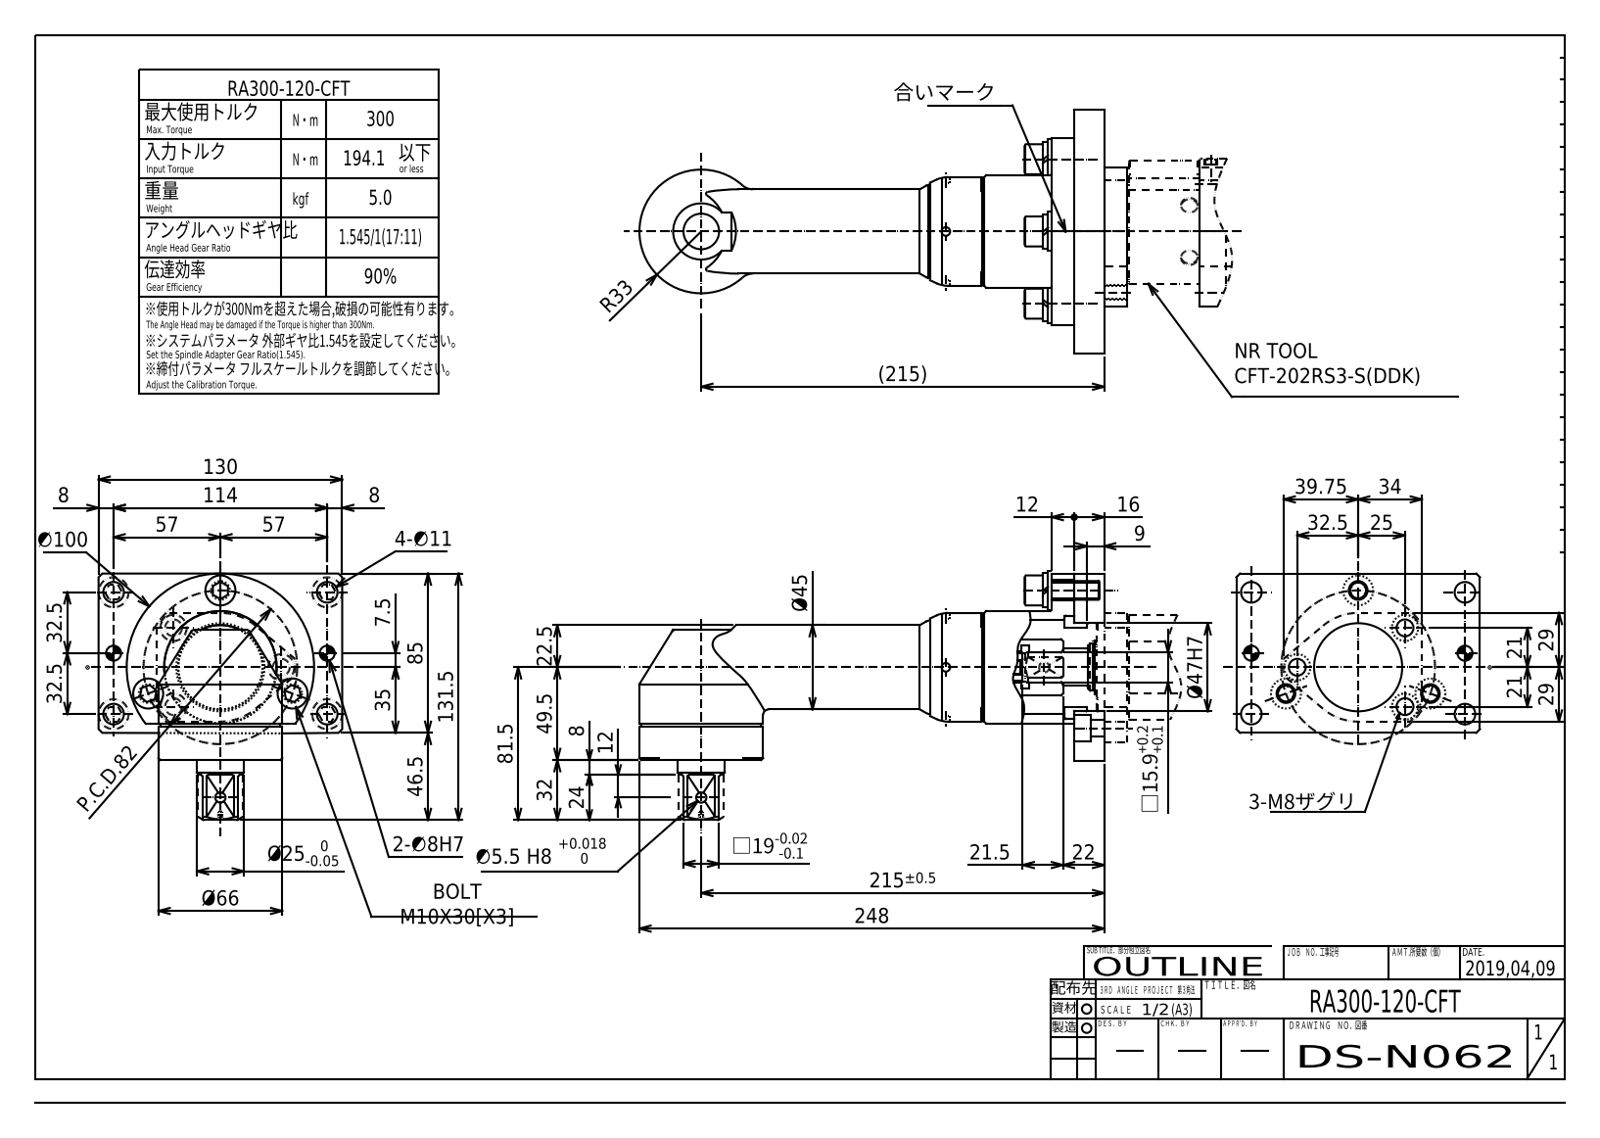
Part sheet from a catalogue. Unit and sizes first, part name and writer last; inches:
Units: inches
Overall size (bounding box): 9.764 × 5.185 × 5.118
Round holes (diameter × count): ⌀0.181 ×6, ⌀0.433 ×4, ⌀0.335 ×3, ⌀0.354 ×3, ⌀0.402 ×3, ⌀0.413 ×3, ⌀0.551 ×3, ⌀0.315 ×2, ⌀0.063 ×1, ⌀0.217 ×1, ⌀0.748 ×1, ⌀0.906 ×1
Round bosses / shafts (diameter × count): ⌀0.724 ×3, ⌀0.709 ×3, ⌀0.63 ×3, ⌀0.394 ×3, ⌀2.598 ×1, ⌀2.52 ×1, ⌀2.362 ×1, ⌀2.283 ×1
Partial cylindrical surfaces — rounded edges, fillets, slot ends (radius × count): R0.039 ×8, R0.207 ×6, R1.407 ×1, R1.821 ×1, R1.969 ×1
Main face-to-face distances: 0.63, 1.102, 0.472, 0.571, 3.917, 0.197, 3.346, 0.276, 1.732, 5.118
Hole centre spacings: 1.28, 0.984, 1.392, 4.667, 1.614, 4.488, 0.846, 1.117
Volume: 43.81 in³ · Surface area: 155.6 in²
Bodies: 1 solid, 252 faces (120 planar, 83 cylindrical, 49 other)
Part name (STEP PRODUCT): RA300-120-CFT(DS-N062)
STEP written by: Autodesk Inventor 2019 (AUTOMOTIVE_DESIGN)
